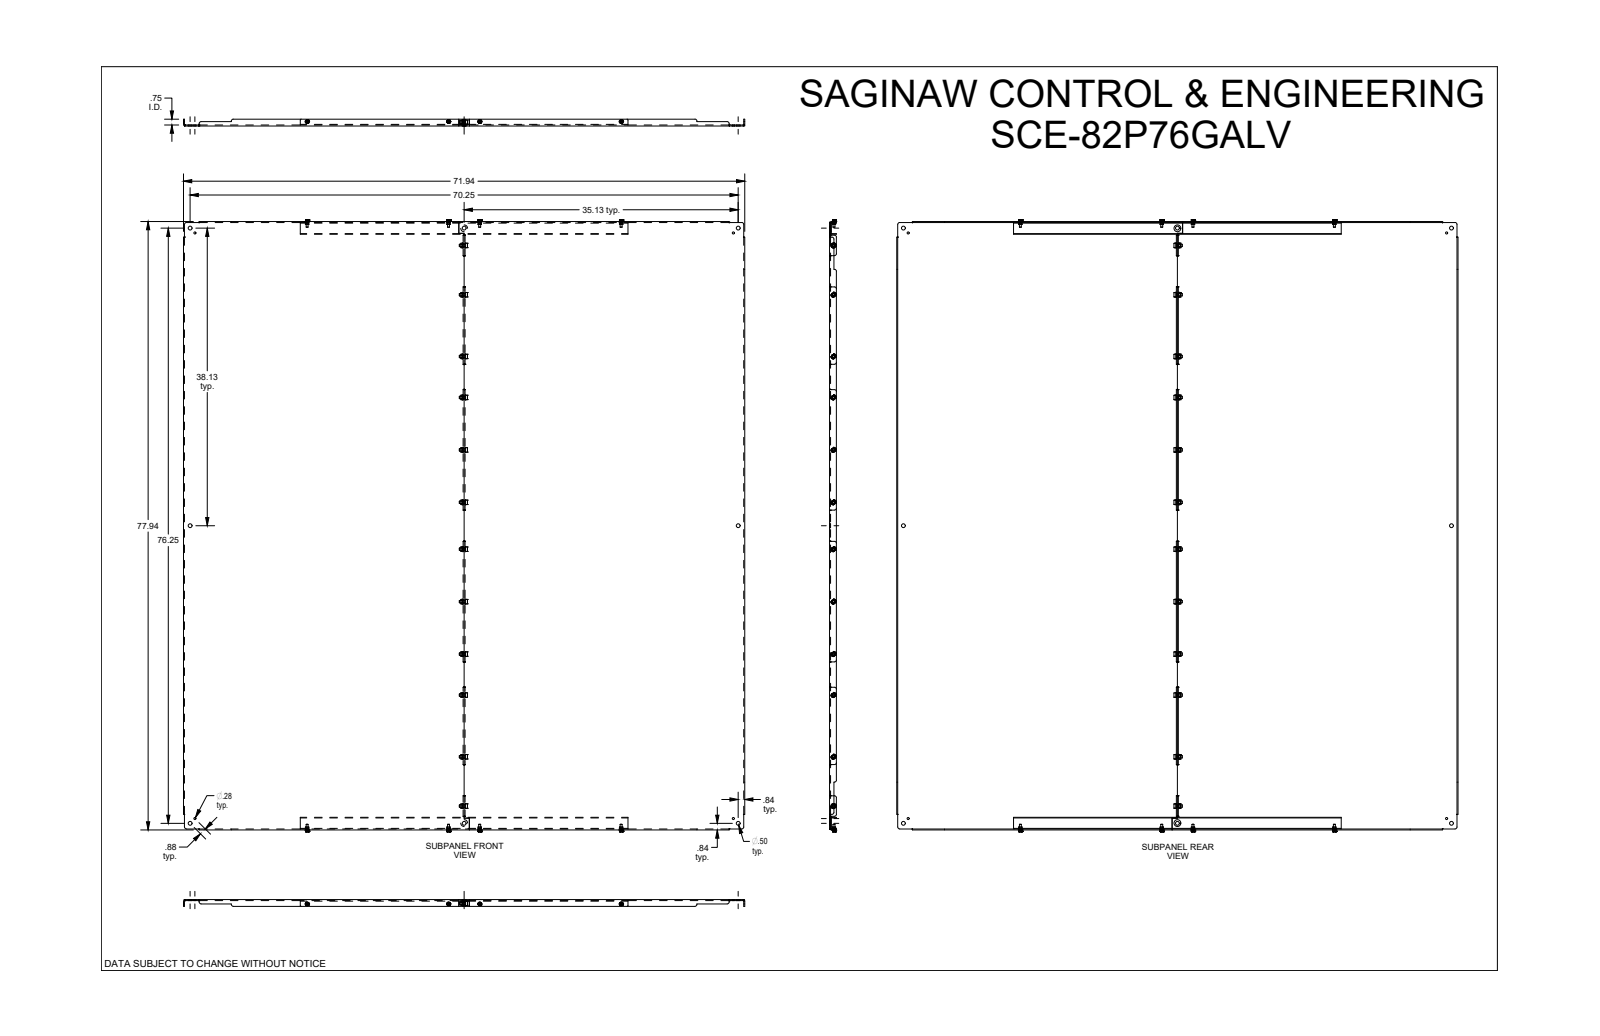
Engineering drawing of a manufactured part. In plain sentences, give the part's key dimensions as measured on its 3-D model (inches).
The part is named "SCE-82P76GALV". Its 3-D file was written by "SolidWorks 2019 (CONFIG_CONTROL_DESIGN)". It is 44 solids with 1922 faces: 528 planar, 478 cylindrical and 916 other. Overall it measures 78.386 by 71.938 by 0.875 inches. Its volume is 752.5 cubic inches and its surface area 12 301 square inches. Round holes: 12 of diameter 0.312, 12 of diameter 0.375, 8 of diameter 0.5, 4 of diameter 0.25, 4 of diameter 0.308, 4 of diameter 0.344, 3 of diameter 0.281, 2 of diameter 0.875, 1 of diameter 0.28. Round bosses or shafts: 12 of diameter 0.31, 4 of diameter 0.5, 4 of diameter 0.44, 4 of diameter 0.343, 4 of diameter 0.248. Partial cylindrical surfaces (rounded edges, fillets, slot ends): 200 of radius 0.01, 24 of radius 0.25, 16 of radius 0.06, 8 of radius 0.172, 6 of radius 0.112, 6 of radius 0.237, 4 of radius 0.08, 4 of radius 0.158. The main face-to-face distances are 0.125, 0.125, 0.078, 35.844, 0.203, 1.422, 76.187, 0.078, 77.813, 35.969. The hole center spacings are 34.511, 34.512, 35.125, 35.125, 37.511, 38.125, 75.634, 79.929.
